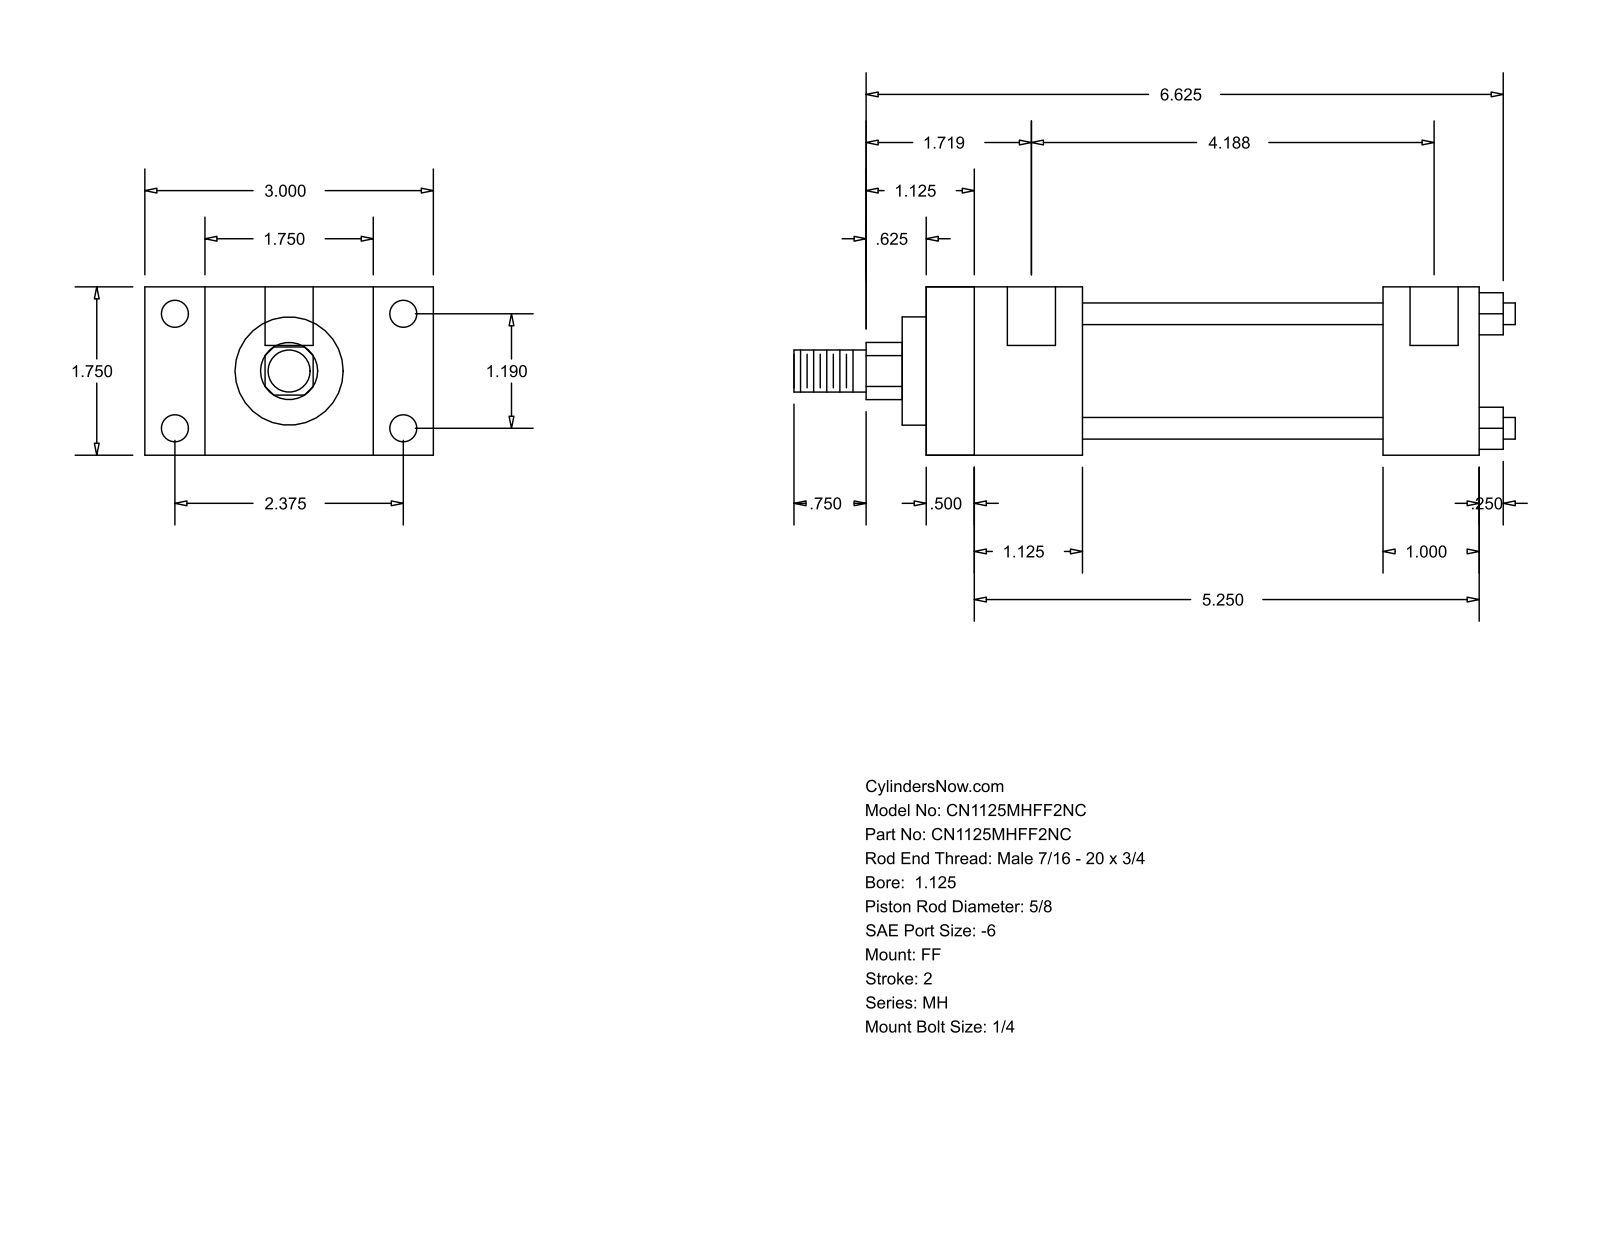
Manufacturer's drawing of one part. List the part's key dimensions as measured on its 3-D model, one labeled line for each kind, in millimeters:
Part name (STEP PRODUCT): MH_FF__0112_0.625
STEP written by: GSSL Pune (CONFIG_CONTROL_DESIGN)
Units: millimetres
Bodies: 0 solids, 92 faces (64 planar, 28 cylindrical, 0 other)
Overall size (bounding box): 190.5 × 76.2 × 44.45
Round holes (diameter × count): ⌀5.56 ×4, ⌀7.14 ×4, ⌀12.7 ×2
Round bosses / shafts (diameter × count): ⌀5.71 ×4, ⌀34.92 ×1, ⌀28.57 ×1, ⌀15.88 ×1, ⌀11.11 ×1
Partial cylindrical surfaces — rounded edges, fillets, slot ends (radius × count): R7.54 ×1
Main face-to-face distances: 44.46, 146.05, 15.87, 12.69, 133.36, 28.58, 60.33, 25.4, 41.27, 120.65
Hole centre spacings: 30.22, 60.32, 67.47, 103.19, 3.17, 106.36
